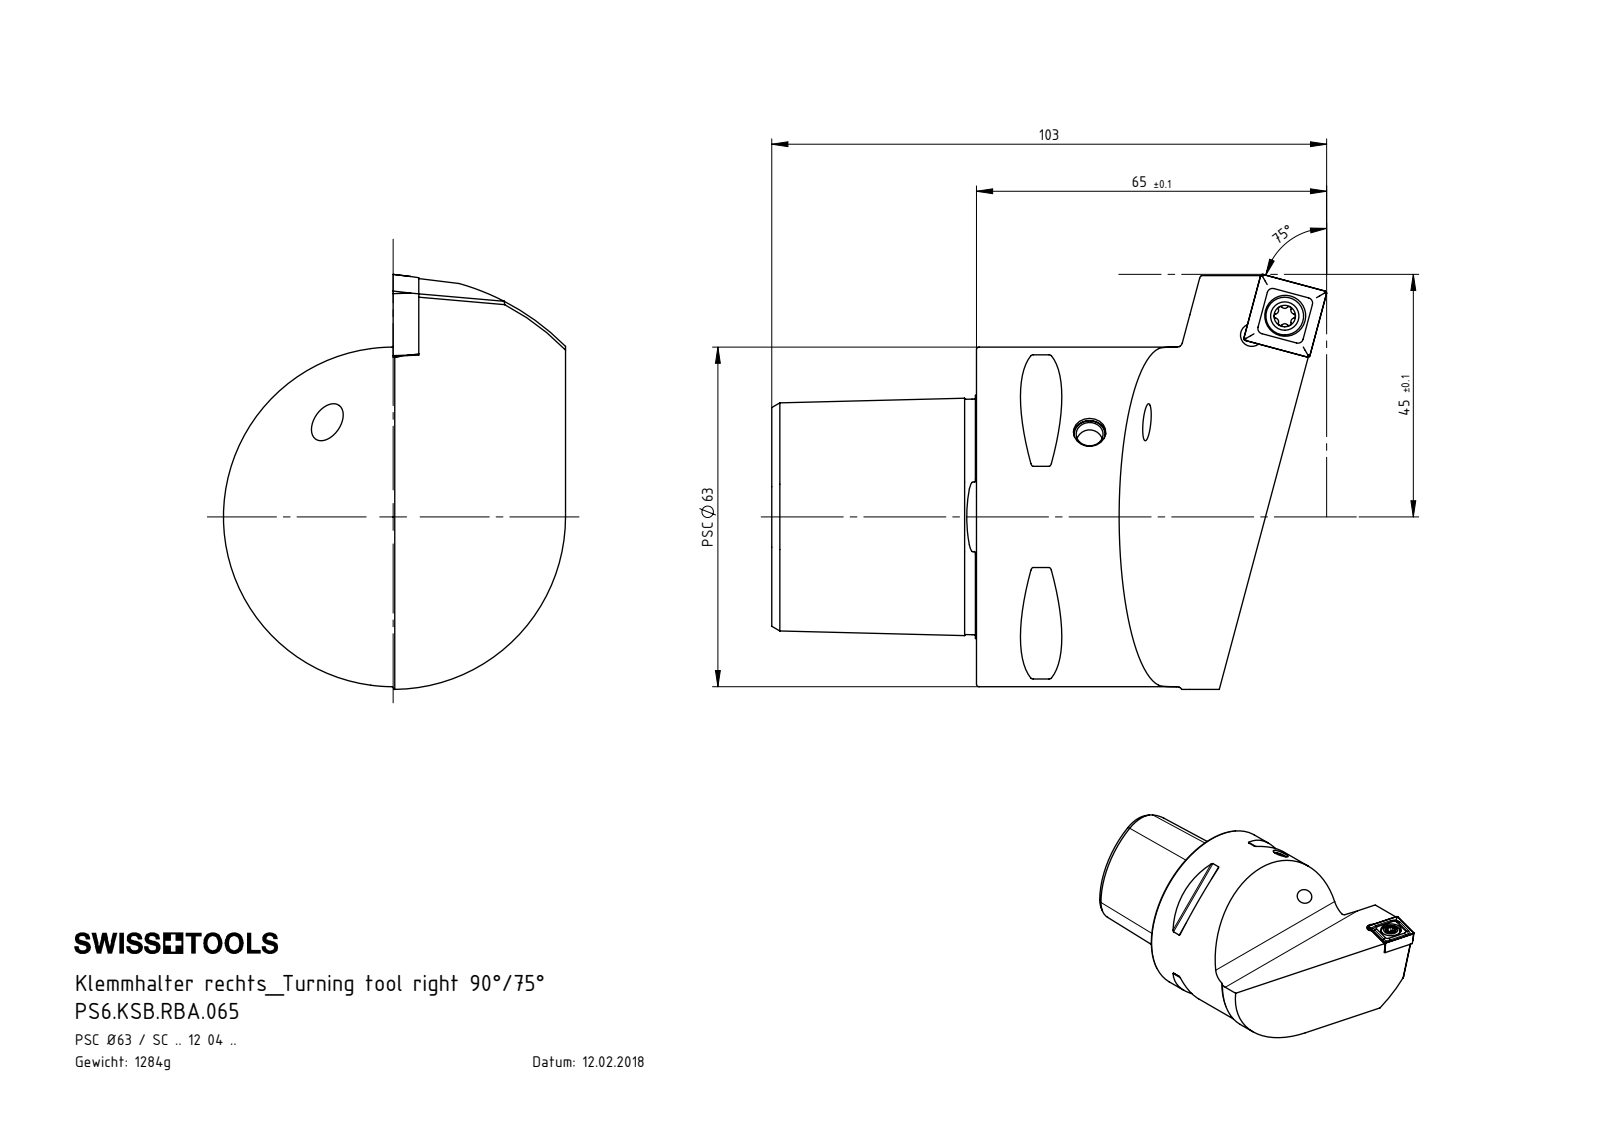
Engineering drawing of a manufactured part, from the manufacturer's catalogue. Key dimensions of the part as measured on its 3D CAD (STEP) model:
Part name (STEP PRODUCT): WCC-ER2.001.010_A; SCMT120404; PS6-KSB.RBA.065_A_Fertigbearbeitung; PS6.KSB.RBA.065 (+1 more)
STEP written by: SolidWorks 2017 (AUTOMOTIVE_DESIGN)
Units: millimetres
Bodies: 5 solids, 267 faces (50 planar, 67 cylindrical, 150 other)
Overall size (bounding box): 103 × 77 × 63.5
Volume: 163 590 mm³ · Surface area: 28 844 mm²
Round holes (diameter × count): ⌀4.2 ×2, ⌀5 ×2, ⌀4 ×1, ⌀5.5 ×1, ⌀7.6 ×1, ⌀8.1 ×1, ⌀18 ×1, ⌀28 ×1, ⌀32 ×1
Round bosses / shafts (diameter × count): ⌀63 ×1, ⌀7 ×1, ⌀6 ×1, ⌀5 ×1
Partial cylindrical surfaces — rounded edges, fillets, slot ends (radius × count): R0.5 ×8, R0.39 ×6, R0.69 ×3, R0.69 ×3, R6 ×2, R32 ×1, R45 ×1
Main face-to-face distances: 31.7, 38, 24.88, 27, 11, 27.24, 4.46, 55.8, 37.8, 10.8
Hole centre spacings: 7.07, 7.17, 27.5, 51.64, 58.59, 58.69, 74.65, 81.71
